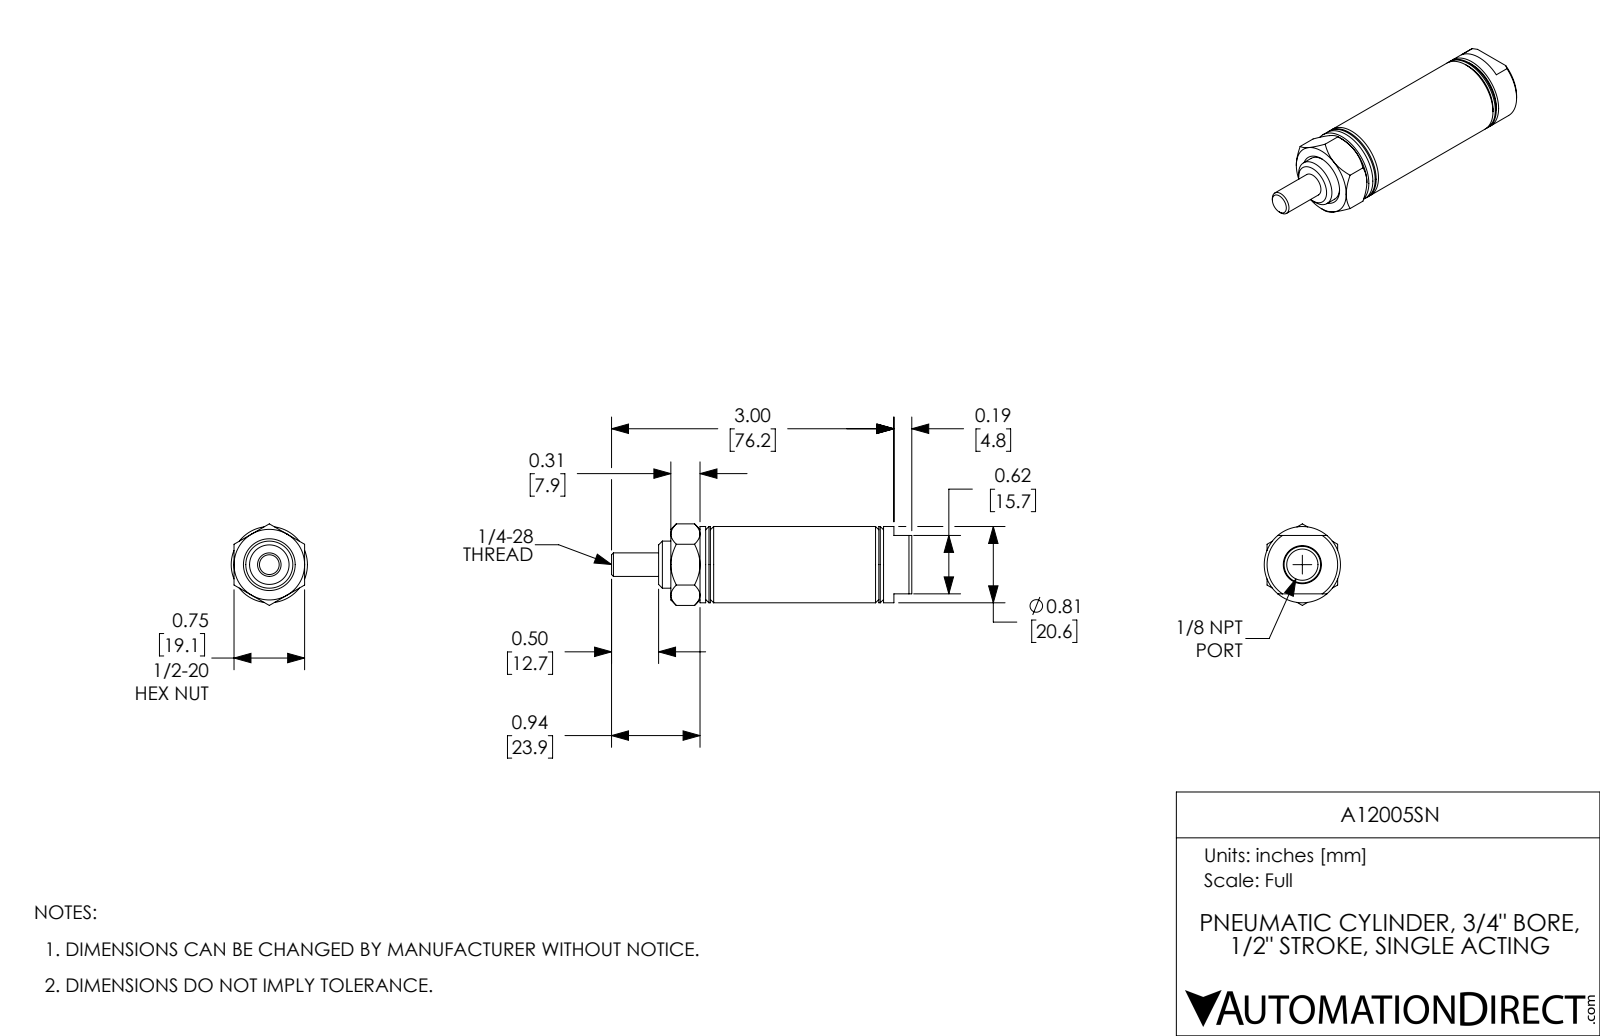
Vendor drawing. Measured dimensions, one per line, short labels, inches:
name: A12005SN; A12005SN_Mounting Nut_D-98; A12005SN-Rod; A12005SN-MainBody
written by: SolidWorks 2017 (AUTOMOTIVE_DESIGN)
unit: in
bodies: 3 solids, 82 faces (25 planar, 24 cylindrical, 33 other)
size: 3.19 × 0.866 × 0.81
volume: 1.076 in³; area: 17.77 in²
holes: 1× ⌀0.25, 1× ⌀0.332, 1× ⌀0.5, 1× ⌀0.75
bosses: 1× ⌀0.81
face distances: 0.5, 1.625, 1, 1.125, 0.625, 0.625, 1.125, 1.625, 2.25, 0.935
